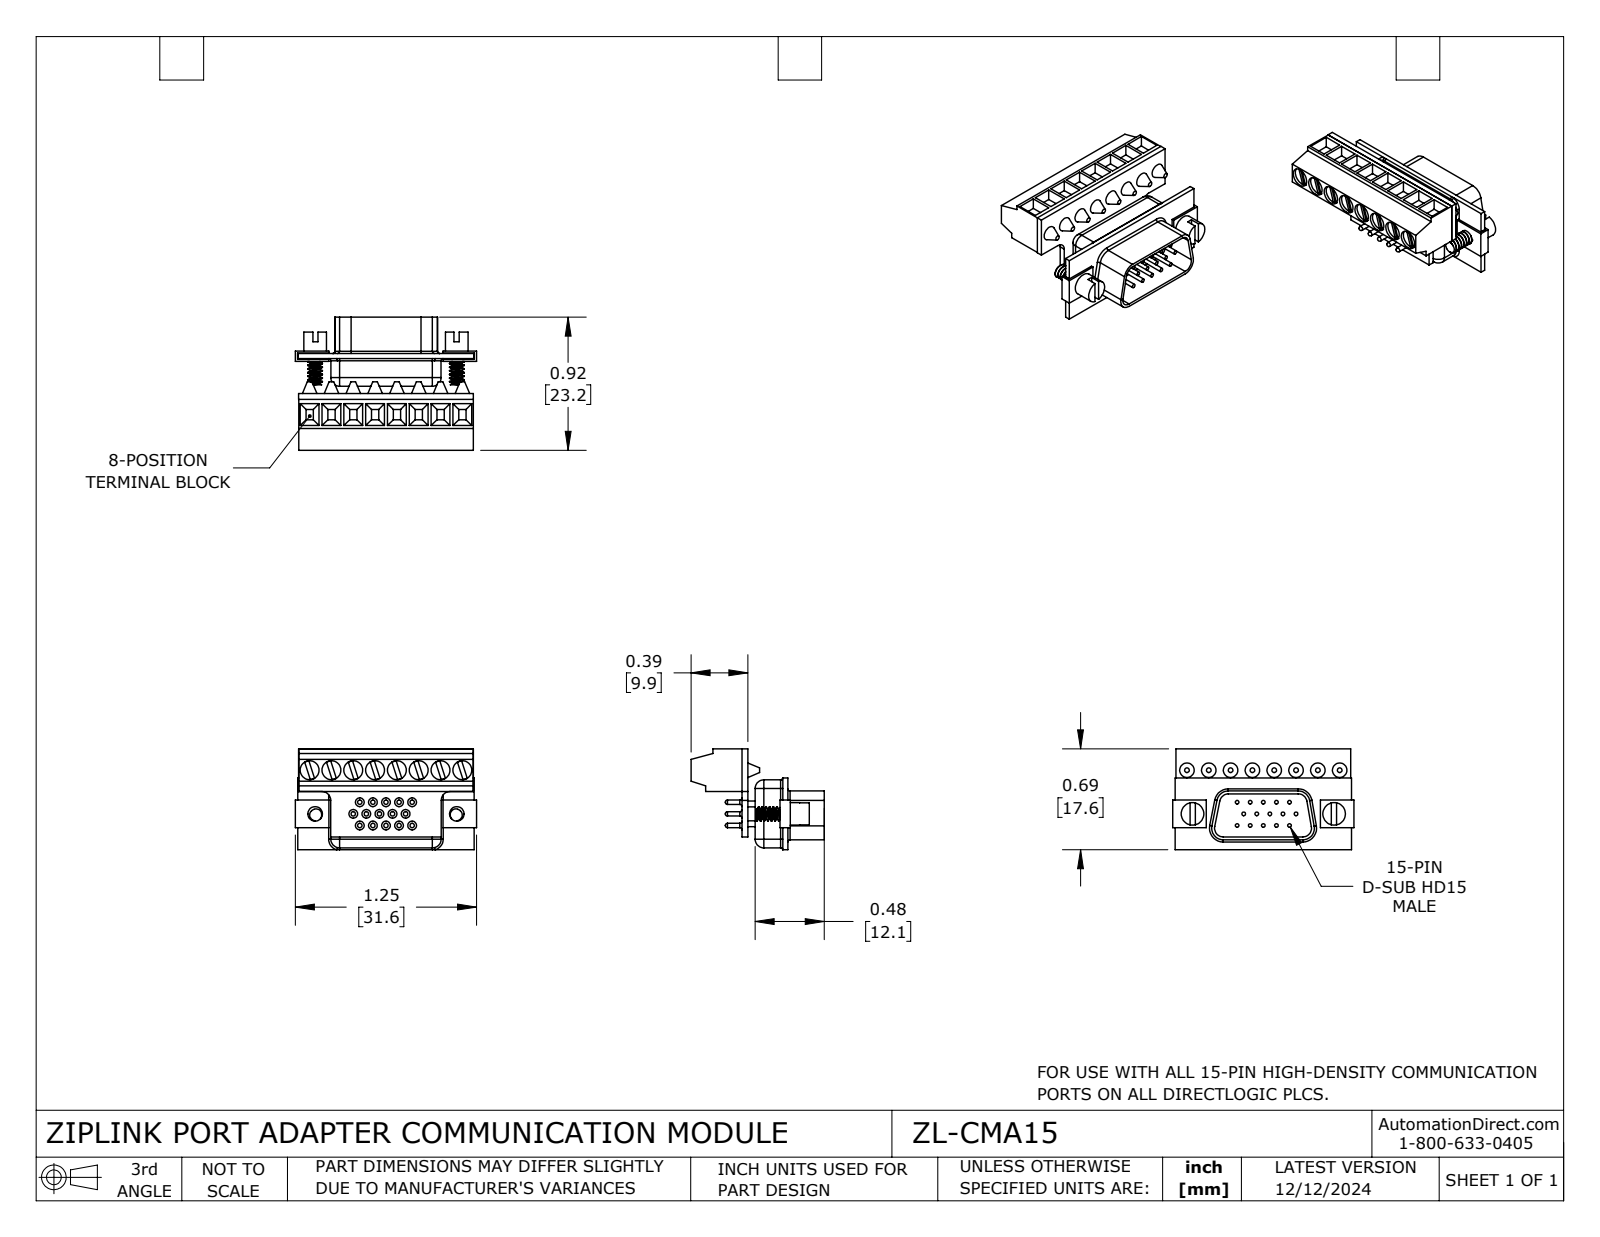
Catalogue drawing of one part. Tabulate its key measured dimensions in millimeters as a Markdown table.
| quantity | value |
| --- | --- |
| part name | ZL-CMA15 |
| STEP written by | SolidWorks 2021 (AUTOMOTIVE_DESIGN) |
| units | millimeters |
| bodies | 2 solids, 446 faces (223 planar, 138 cylindrical, 85 other) |
| overall size | 31.6 × 23.2 × 17.6 |
| volume | 3 900 mm³ |
| surface area | 3 940 mm² |
| round holes (diameter × count) | 3.3 × 8 |
| round bosses / shafts (diameter × count) | 0.8 × 15, 0.6 × 15, 3.9 × 2, 2.5 × 2 |
| partial cylindrical surfaces (radius × count) | 1.5 × 14, 0.4 × 8, 1 × 4, 2 × 4 |
| main face-to-face distances | 7, 0.5, 0.9, 8, 8, 1, 6.1, 7.1, 1.3, 8.4 |
| hole center spacings | 3.8, 7.6, 11.4, 15.2, 19.1, 22.9, 26.7 |
